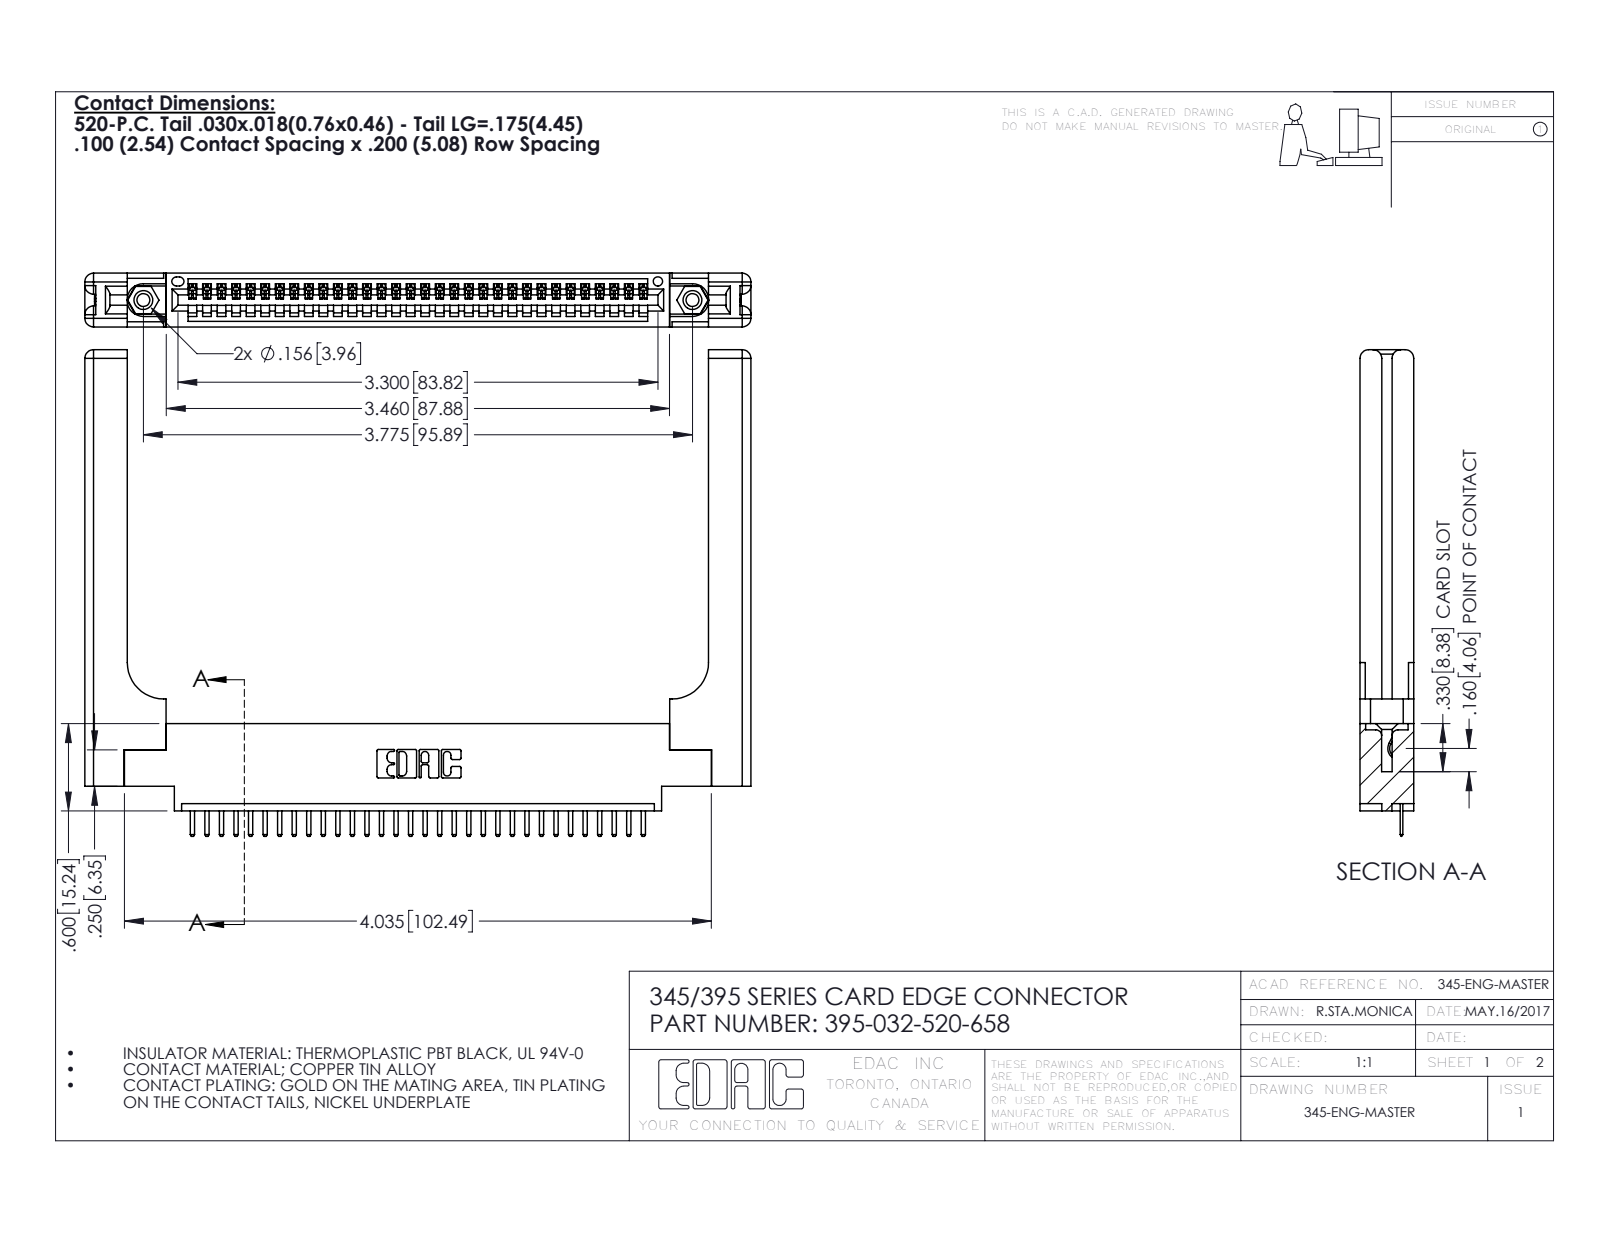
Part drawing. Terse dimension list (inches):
name: 345-220-058_345-220-058; 345 Part_0.170 Offset - 0.156 Dia-TH; 345-292-001_345-293-120; 395-032-520-658 (+1 more)
written by: SolidWorks 2016 (CONFIG_CONTROL_DESIGN)
unit: in
bodies: 37 solids, 2370 faces (1576 planar, 734 cylindrical, 60 other)
size: 4.579 × 3.345 × 0.37
volume: 1.176 in³; area: 29.91 in²
holes: 2× ⌀0.089, 2× ⌀0.125, 2× ⌀0.156, 1× ⌀0.064
bosses: 2× ⌀0.155
rounds: 66× R0.01, 64× R0.006, 22× R0.01, 16× R0.06, 6× R0.007, 6× R0.031, 3× R0.026, 2× R0.03
face distances: 0.37, 0.072, 0.298, 0.148, 0.15, 0.098, 0.272, 0.025, 0.2, 0.077
hole spacings: 0.27, 3.54, 3.775
